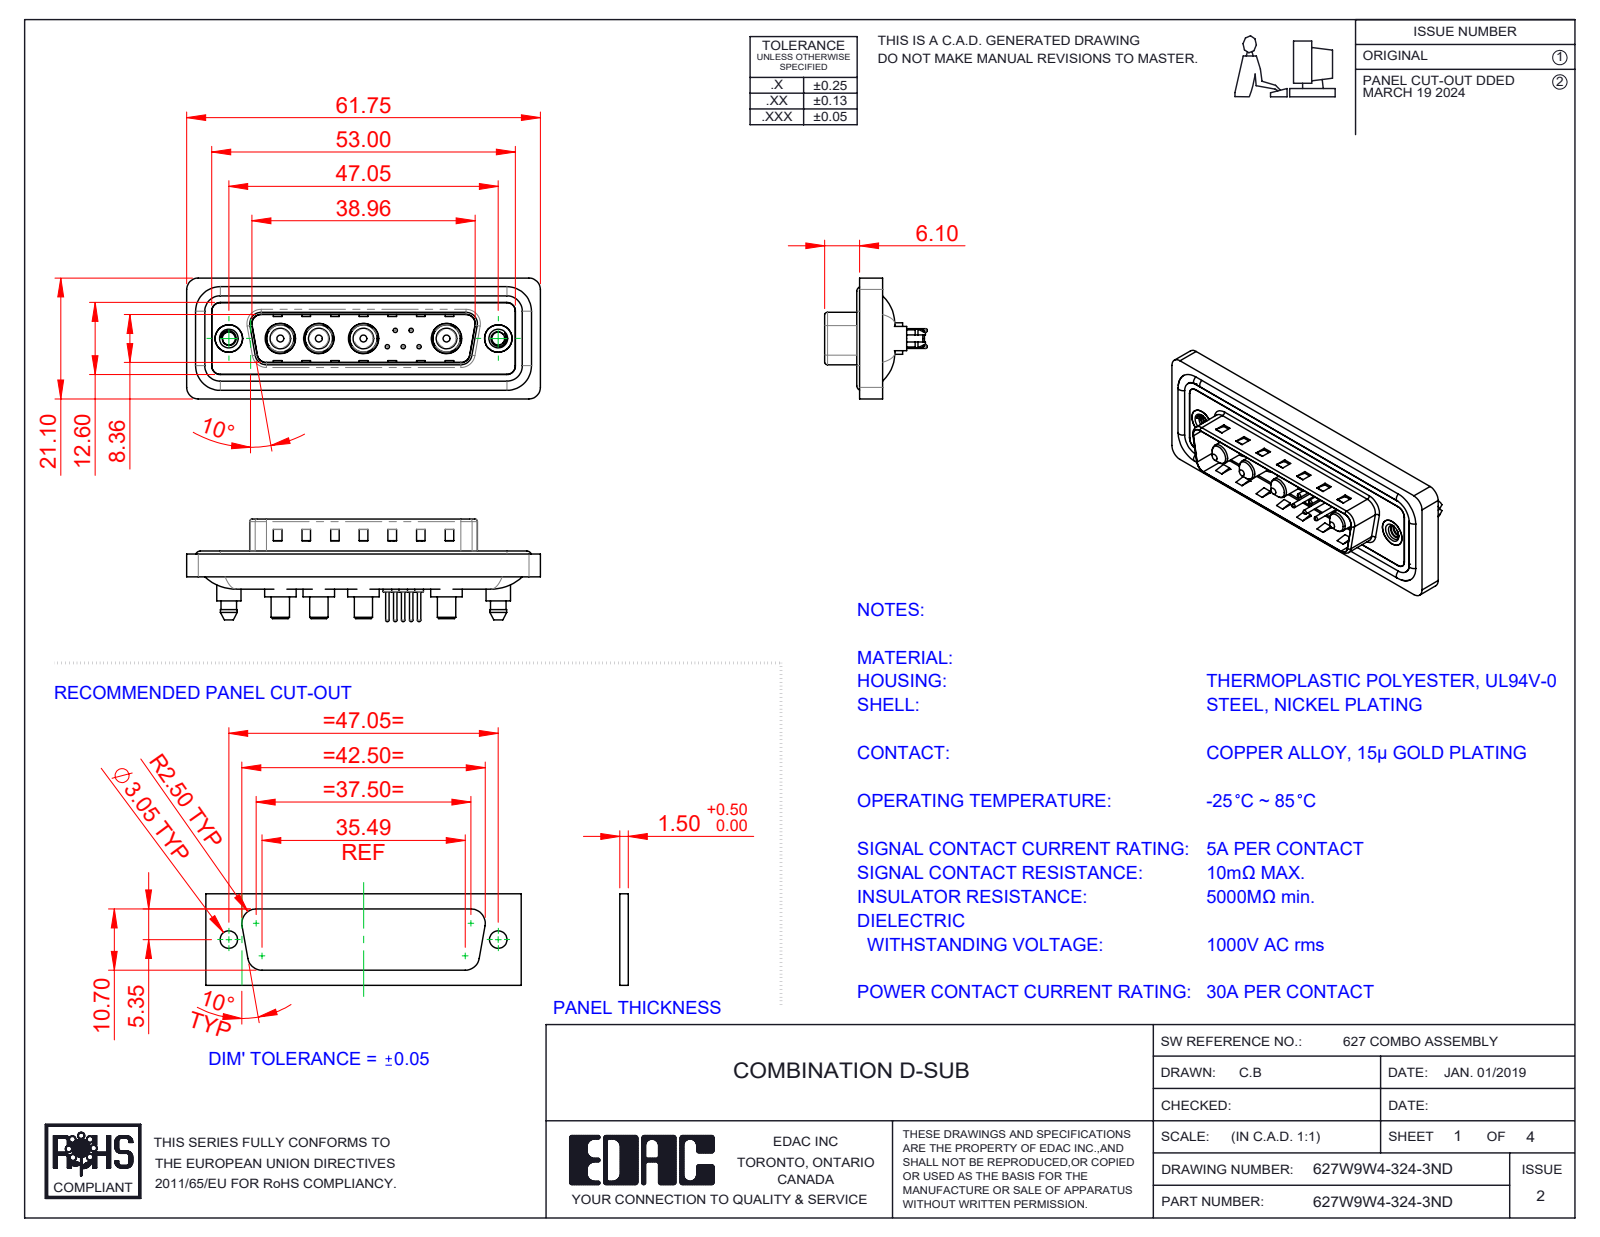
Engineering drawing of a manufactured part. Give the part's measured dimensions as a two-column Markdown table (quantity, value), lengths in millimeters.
| quantity | value |
| --- | --- |
| part name | 627Combo Threaded Boardlock_D; 627Combo Shell Front_25 Contacts; 627Combo Housing_9W4; 627Combo Shell Rear_25 Contacts (+6 more) |
| STEP written by | SolidWorks 2023 (CONFIG_CONTROL_DESIGN) |
| units | millimeters |
| bodies | 20 solids, 882 faces (300 planar, 374 cylindrical, 208 other) |
| overall size | 61.75 × 21.1 × 17.9 |
| volume | 7 567 mm³ |
| surface area | 12 190 mm² |
| round holes (diameter × count) | 0.75 × 5, 1.6 × 5, 2 × 5, 4.85 × 4, 5.3 × 4, 2.26 × 2, 4 × 2, 4.8 × 2, 5 × 2 |
| round bosses / shafts (diameter × count) | 1.5 × 5, 0.6 × 5, 5.5 × 4, 5.2 × 4, 4.75 × 4, 3.75 × 4, 3.6 × 4, 3.2 × 4 |
| partial cylindrical surfaces (radius × count) | 1.5 × 24, 2 × 18, 1.6 × 10, 0.5 × 8, 0.25 × 4, 0.6 × 4, 0.65 × 4, 0.9 × 4 |
| main face-to-face distances | 0.4, 1.5, 1.1, 0.5, 3.1, 1.6, 2.9, 0.82, 9.58, 5.65 |
| hole center spacings | 3.16, 2.77, 5.04, 14.51, 2.78, 4.4, 4.41, 5 |
